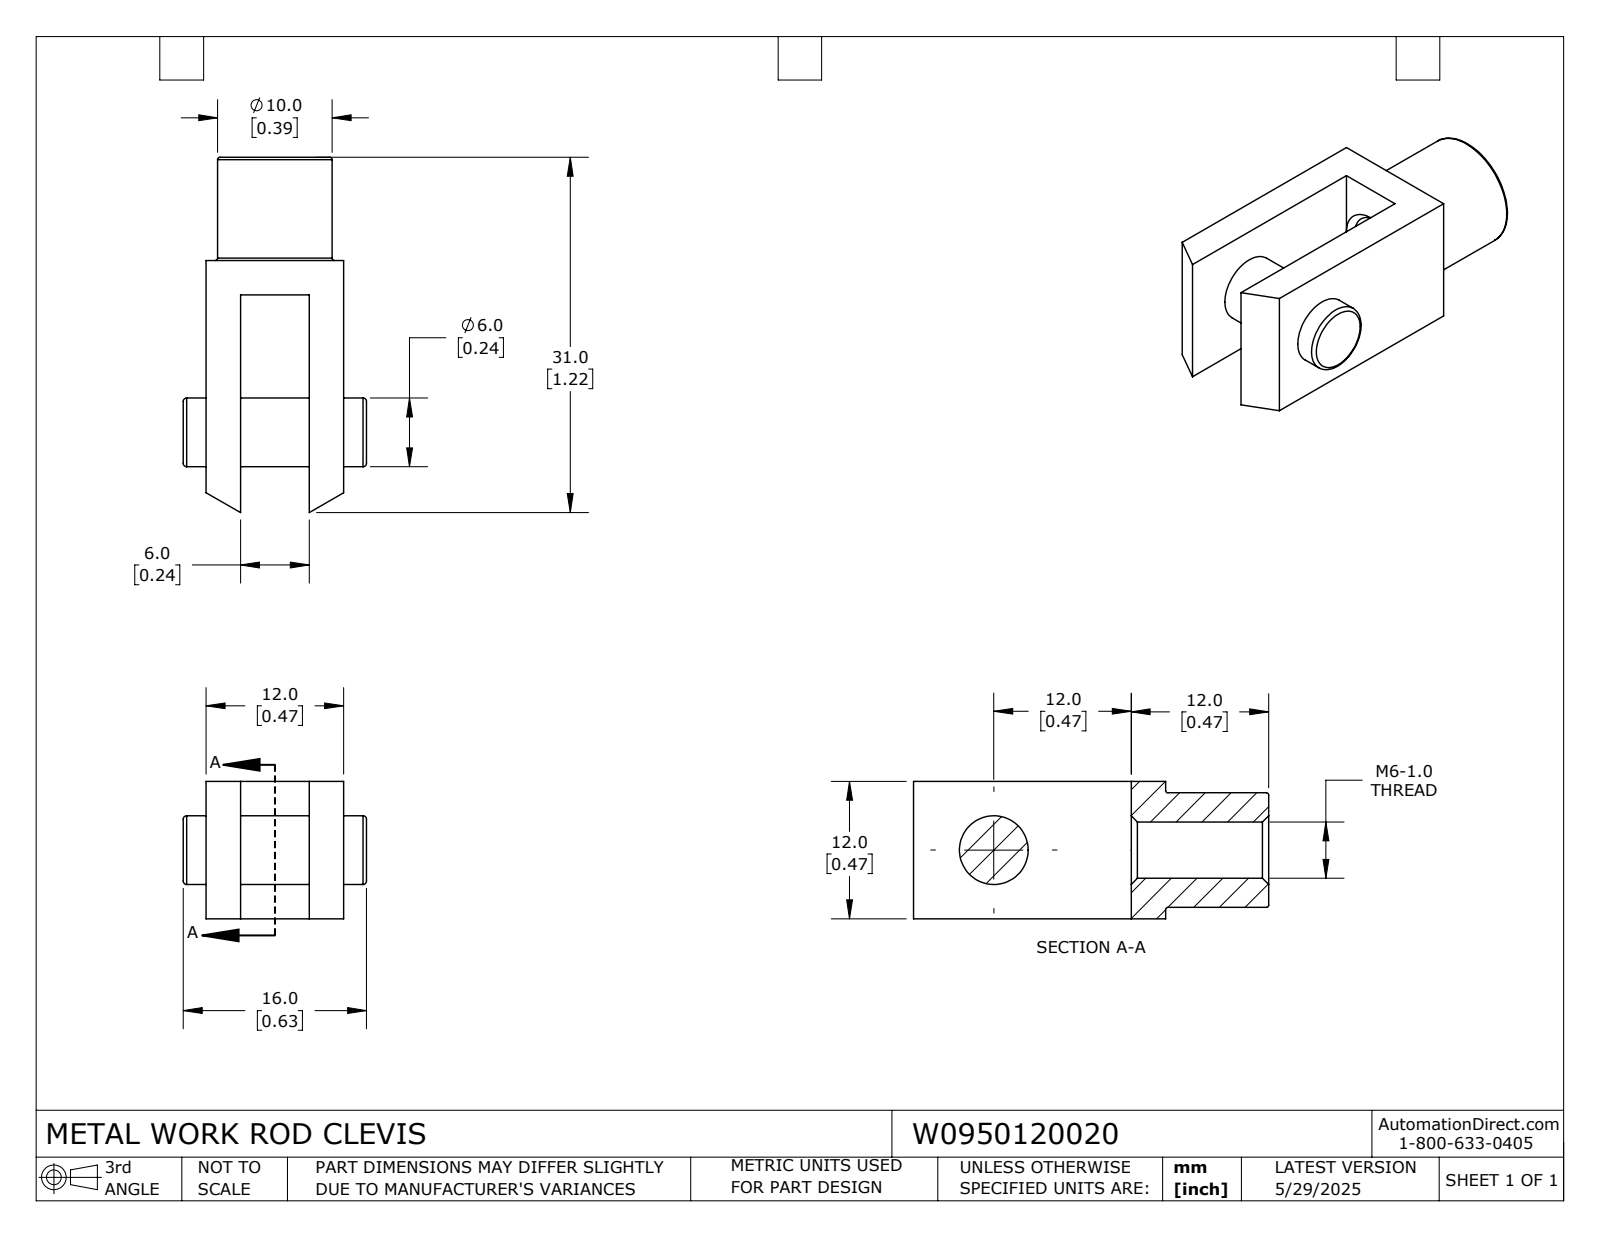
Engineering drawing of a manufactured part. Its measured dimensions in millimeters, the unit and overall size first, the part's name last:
Units: millimetres
Overall size (bounding box): 31 × 16 × 12
Round holes (diameter × count): ⌀4.92 ×1
Round bosses / shafts (diameter × count): ⌀10 ×1, ⌀6 ×1
Main face-to-face distances: 9, 3, 12, 6, 2, 5, 11, 14, 16
Volume: 2 494 mm³ · Surface area: 2 074 mm²
Bodies: 1 solid, 36 faces (14 planar, 10 cylindrical, 12 other)
Part name (STEP PRODUCT): W0950120020
STEP written by: SolidWorks 2024 (CONFIG_CONTROL_DESIGN)
